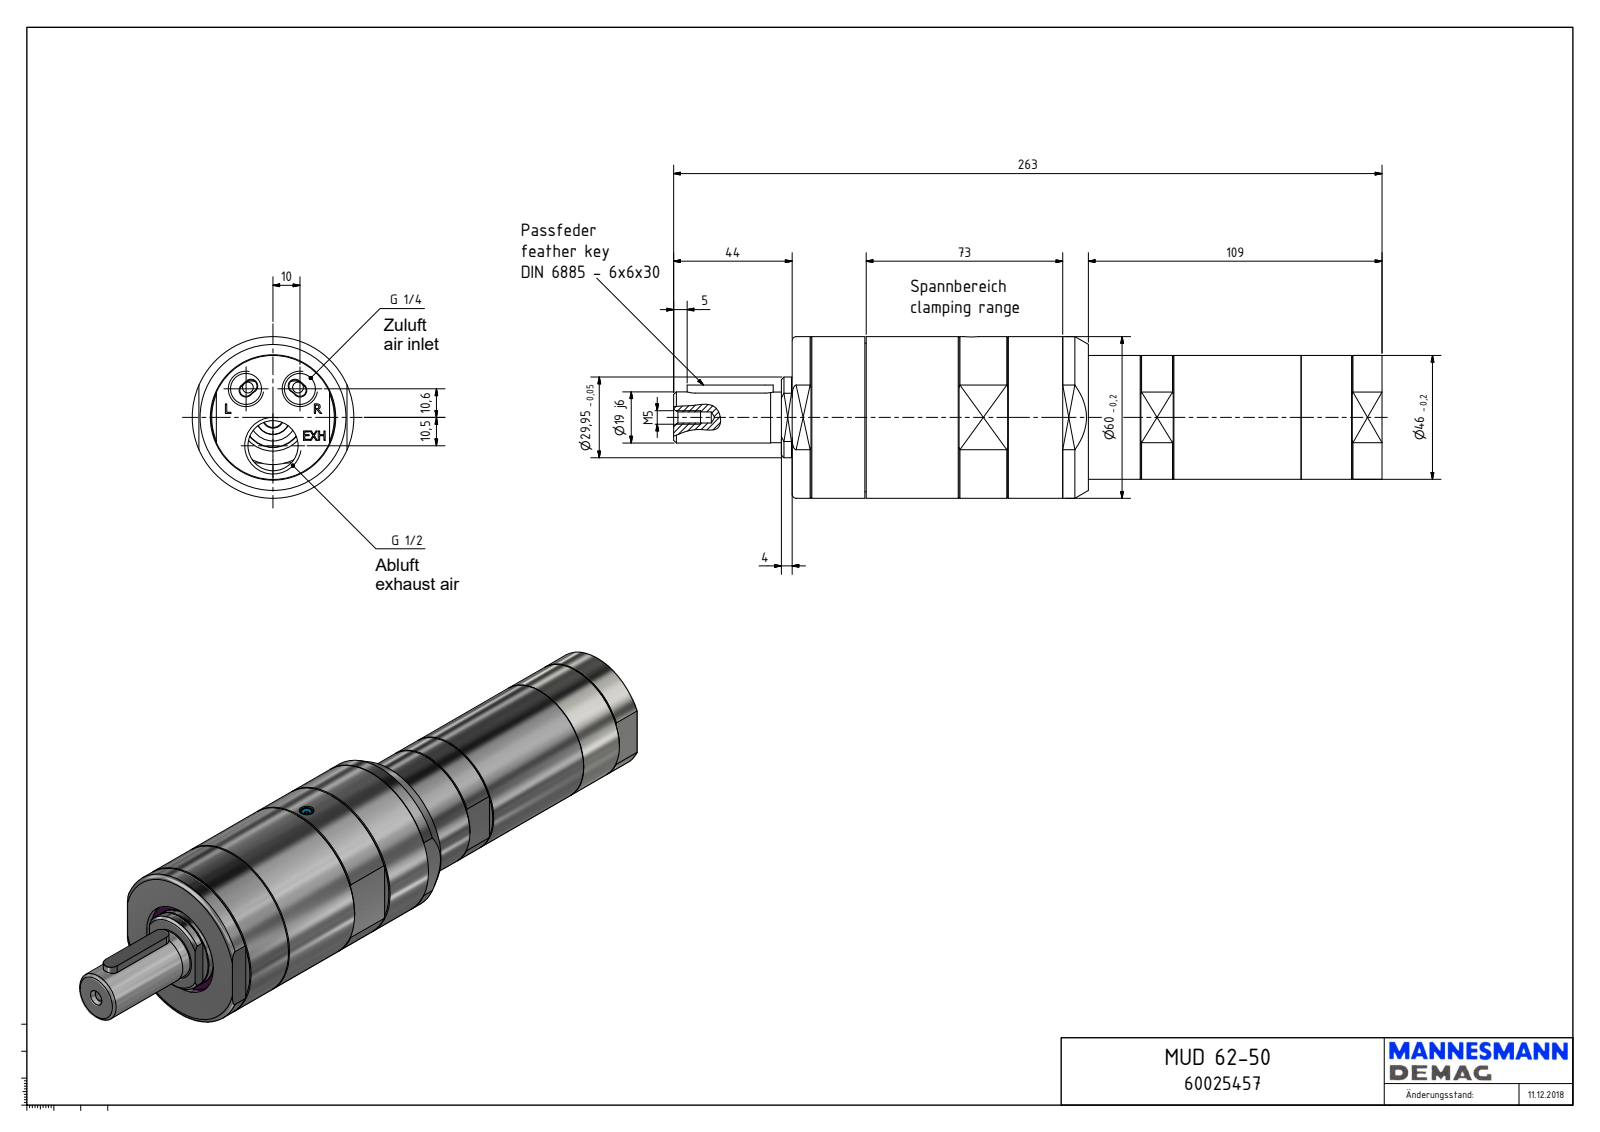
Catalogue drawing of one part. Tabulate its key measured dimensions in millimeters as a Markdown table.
| quantity | value |
| --- | --- |
| part name | MUD 62-50_60025457 |
| STEP written by | Autodesk Inventor 2018 (AUTOMOTIVE_DESIGN) |
| units | millimeters |
| bodies | 1 solid, 227 faces (120 planar, 54 cylindrical, 53 other) |
| overall size | 263 × 60 × 60 |
| volume | 494 285 mm³ |
| surface area | 53 406 mm² |
| round holes (diameter × count) | 11.45 × 2, 1.55 × 1, 4 × 1, 4.13 × 1, 5.5 × 1, 18.63 × 1, 35 × 1, 36.5 × 1, 40 × 1, 46.5 × 1, 55.38 × 1 |
| round bosses / shafts (diameter × count) | 60 × 1, 55.18 × 1, 46 × 1, 33.14 × 1, 29.95 × 1, 19 × 1, 18.8 × 1, 5 × 1 |
| partial cylindrical surfaces (radius × count) | 2.5 × 4, 3 × 2, 5 × 2, 16.75 × 1, 19 × 1, 26.3 × 1 |
| main face-to-face distances | 6.5, 107.5, 219, 48.5, 55, 101, 0.5, 76, 110, 109 |
| hole center spacings | 14.57, 23.35, 10.5, 20 |
